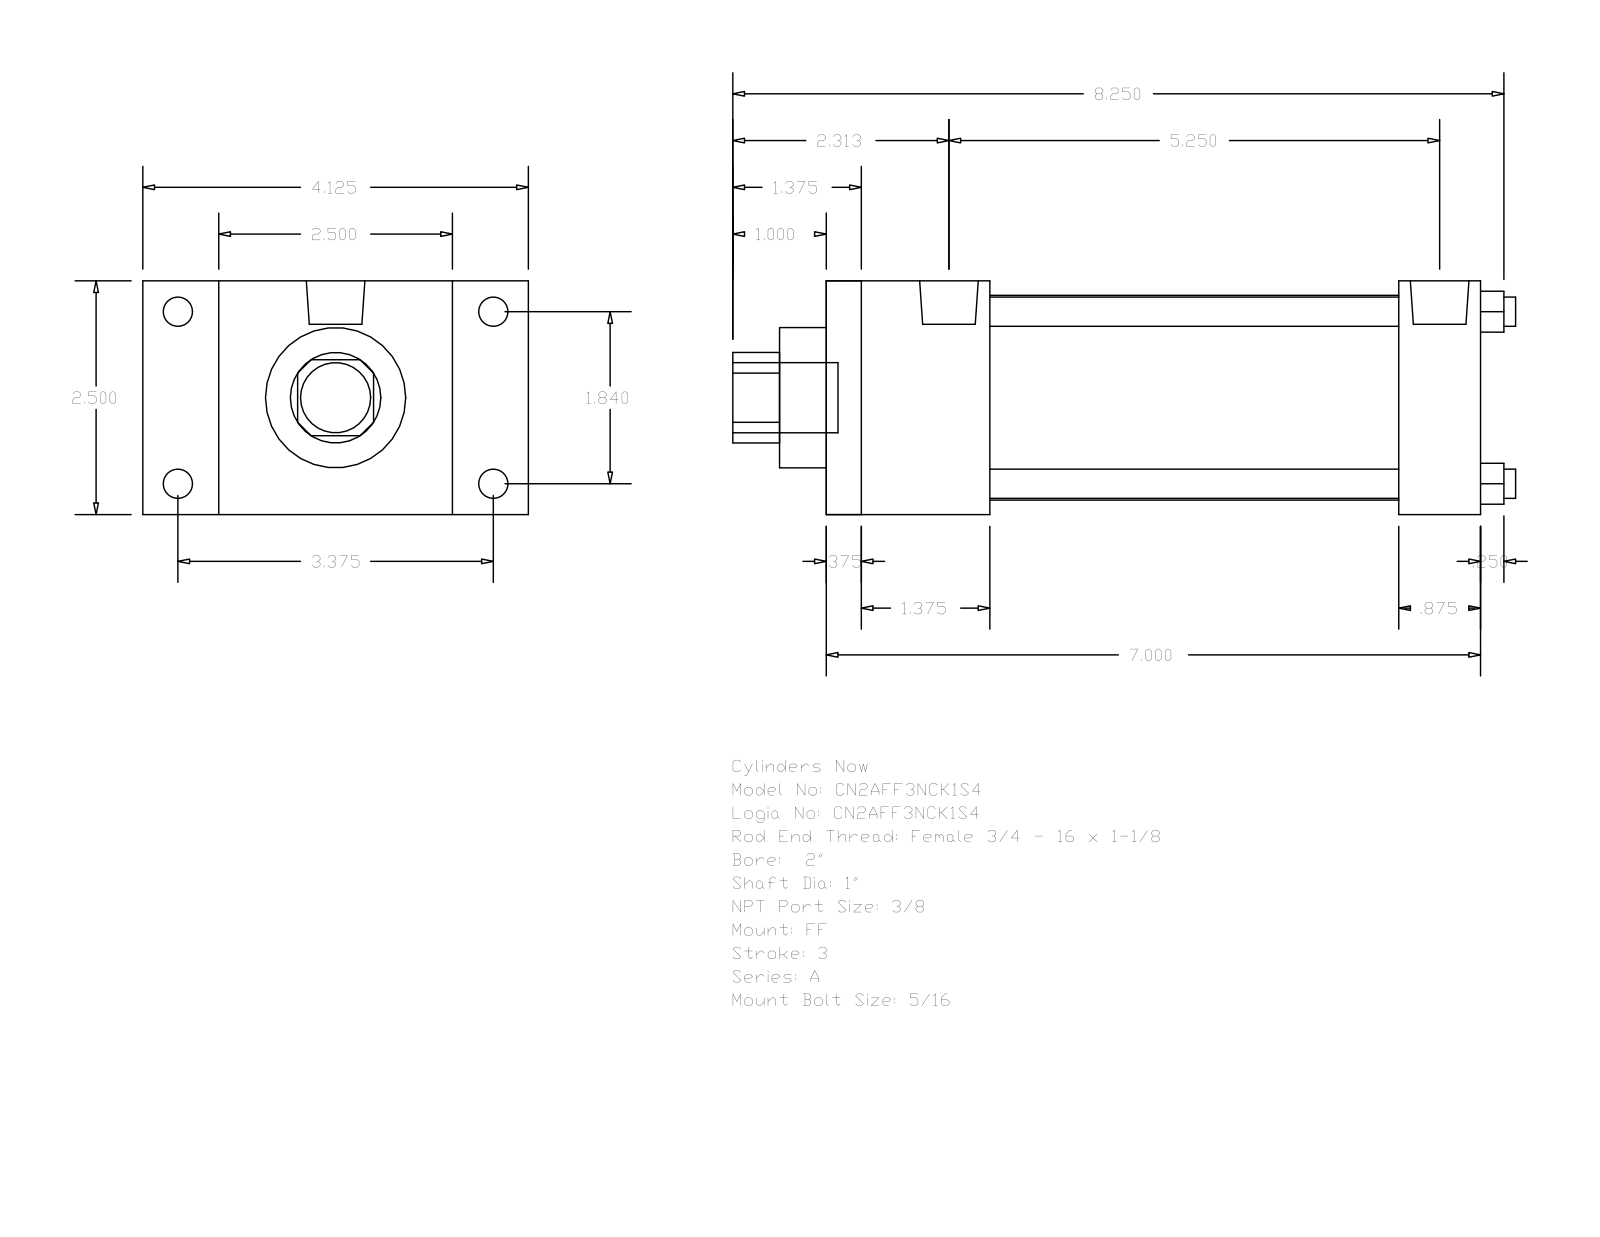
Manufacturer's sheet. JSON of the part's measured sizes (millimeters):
{"part_name": "A_FF__0200_1", "step_written_by": "GSSL Pune (CONFIG_CONTROL_DESIGN)", "units": "millimeters", "bodies": {"solids": 0, "faces": 92, "planar": 64, "cylindrical": 28, "other": 0}, "overall_size": [212.72, 104.78, 63.5], "round_holes": [[7.94, 4], [25.4, 1], [38.1, 1], [55.63, 1]], "round_bosses_or_shafts": [[7.94, 4], [5.56, 4], [15.93, 2], [19.05, 1]], "partial_cylinders_radius": [[12.29, 1]], "face_to_face_distances": [63.5, 177.8, 9.52, 168.28, 20.64, 44.45, 155.57, 34.93, 146.05, 111.12], "hole_center_spacings": [33.05, 46.74, 66.1]}
